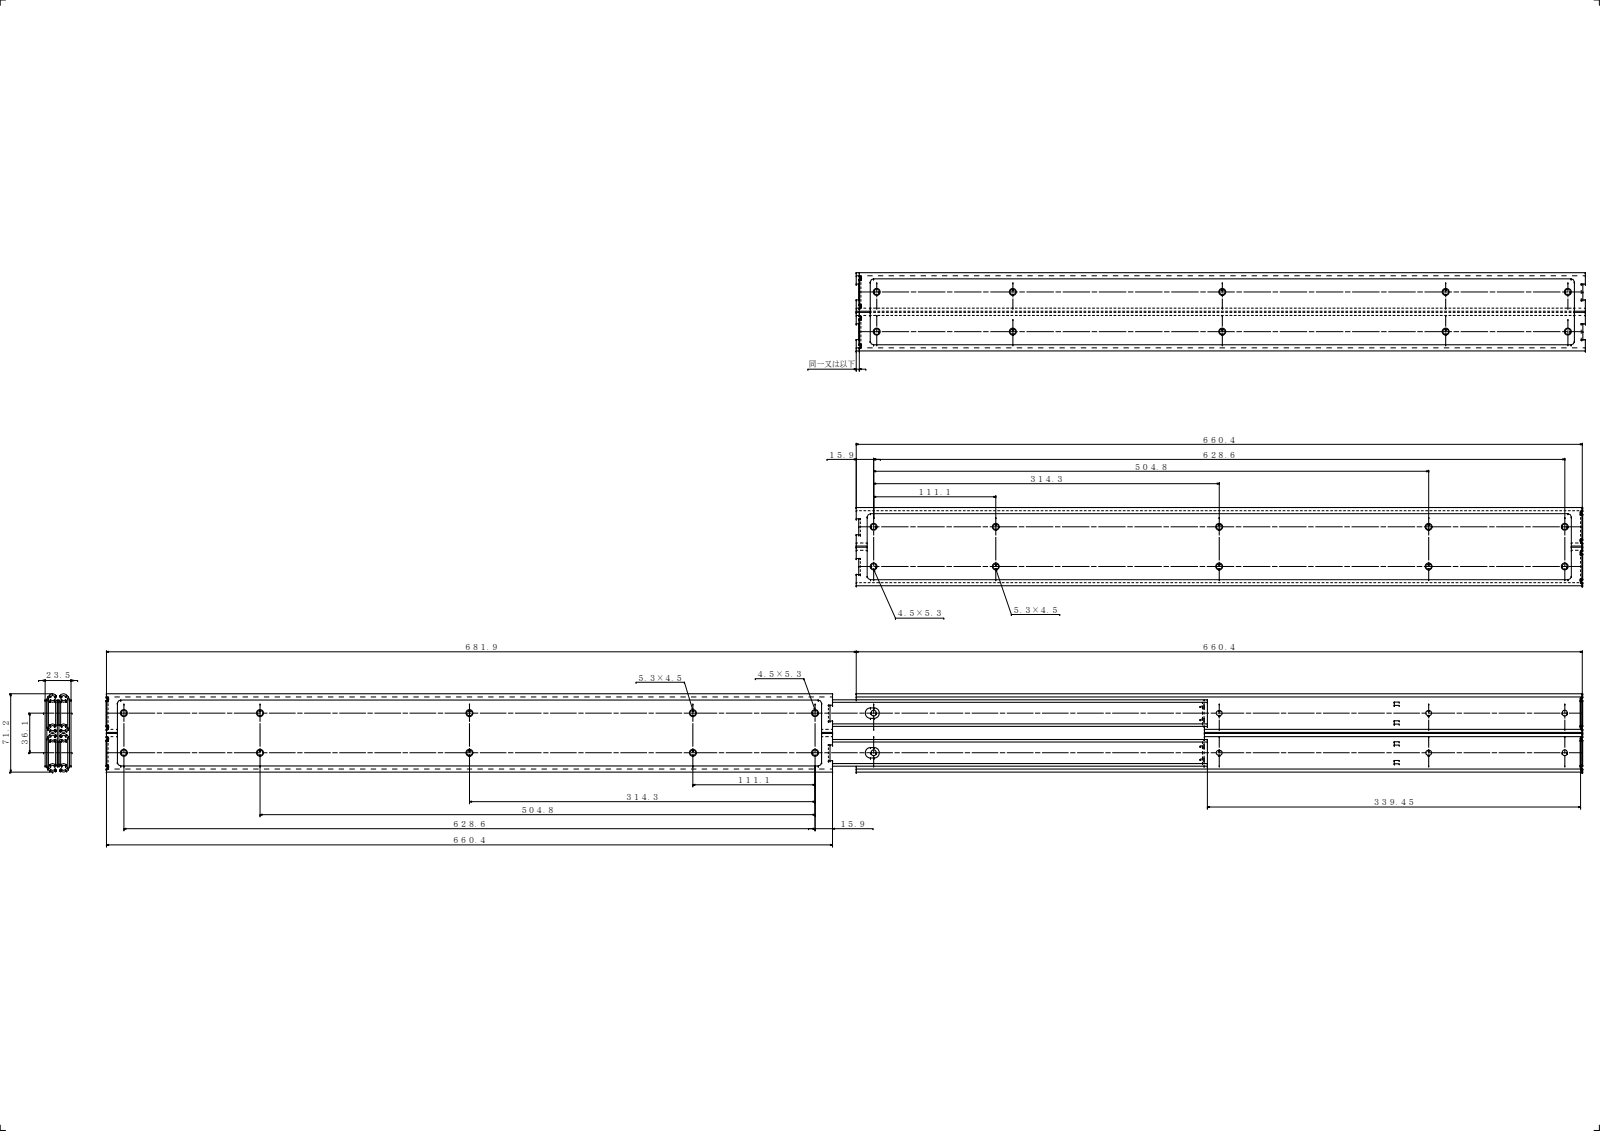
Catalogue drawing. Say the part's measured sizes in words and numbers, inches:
The part is named "OM U51-26; IM U51-26; U51-26; OM継板-26 (+1 more)". Its 3-D file was written by "SolidWorks 2019 (CONFIG_CONTROL_DESIGN)". It is 11 solids with 652 faces: 310 planar, 342 cylindrical and 0 other. Overall it measures 52.846 by 2.803 by 0.925 inches. Its volume is 29.6 cubic inches and its surface area 1 041 square inches. Round holes: 24 of diameter 0.252, 2 of diameter 0.256. Partial cylindrical surfaces (rounded edges, fillets, slot ends): 40 of radius 0.089, 32 of radius 0.039, 24 of radius 0.016, 24 of radius 0.079, 24 of radius 0.118, 12 of radius 0.157, 8 of radius 0.012, 8 of radius 0.051. The main face-to-face distances are 0.059, 0.433, 0.374, 0.807, 0.492, 0.118, 0.315, 0.866, 0.748, 0.256. The hole center spacings are 1.421, 12.374, 12.456, 26.846, 26.884, 2, 2.374, 2.454.
